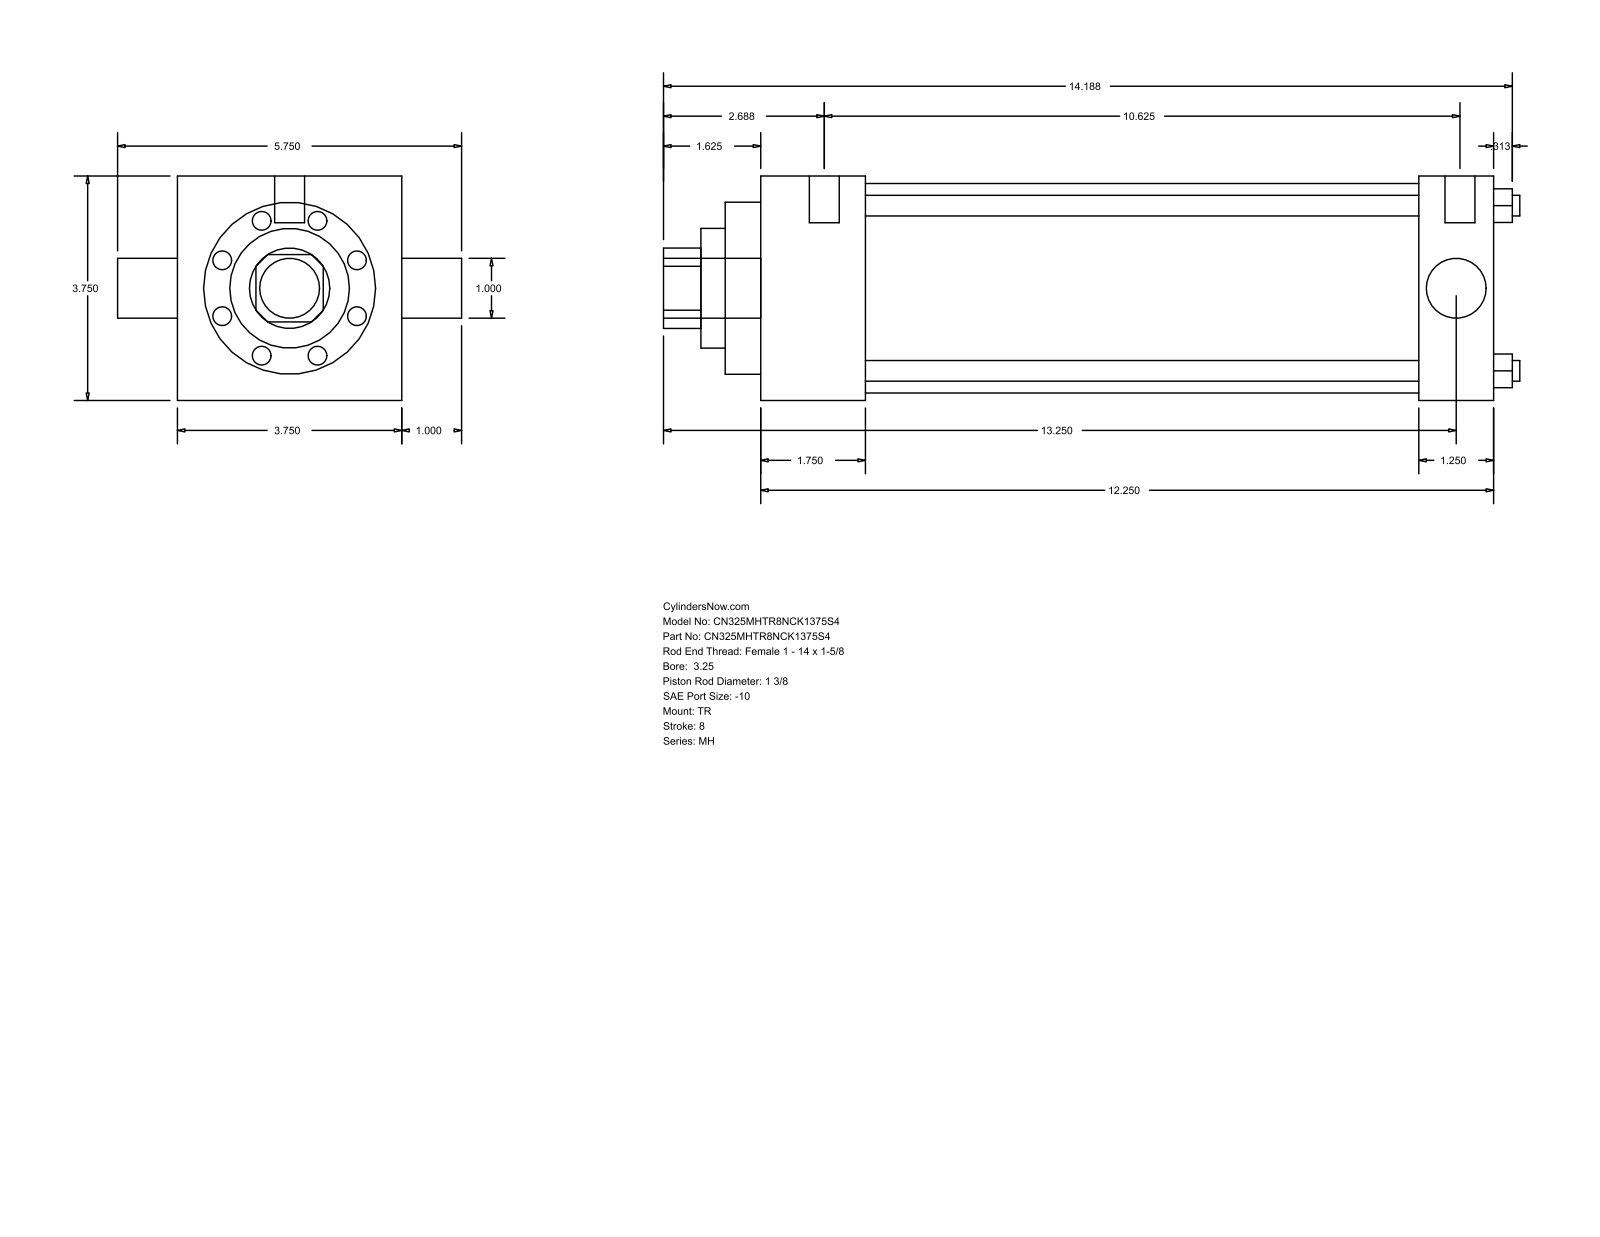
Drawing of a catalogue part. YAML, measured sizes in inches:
part_name: "MH_TR__0325_1.375"
step_written_by: "GSSL Pune (CONFIG_CONTROL_DESIGN)"
units: inches
bodies: {solids: 0, faces: 86, planar: 61, cylindrical: 25, other: 0}
overall_size: [14.313, 5.75, 3.75]
round_holes:
  - {diameter: 0.345, count: 4}
  - {diameter: 1, count: 1}
  - {diameter: 1.375, count: 1}
  - {diameter: 2, count: 1}
  - {diameter: 2.875, count: 1}
  - {diameter: 3.5, count: 1}
round_bosses_or_shafts:
  - {diameter: 0.219, count: 3}
  - {diameter: 0.5, count: 2}
  - {diameter: 1, count: 1}
partial_cylinders:
  - {radius: 0.672, count: 1}
face_to_face_distances: [3.75, 12.25, 1.75, 11, 9.25, 10.5, 1.25, 0.594, 2.344, 11.594]
hole_center_spacings: [1.952, 2.76, 3.903]
